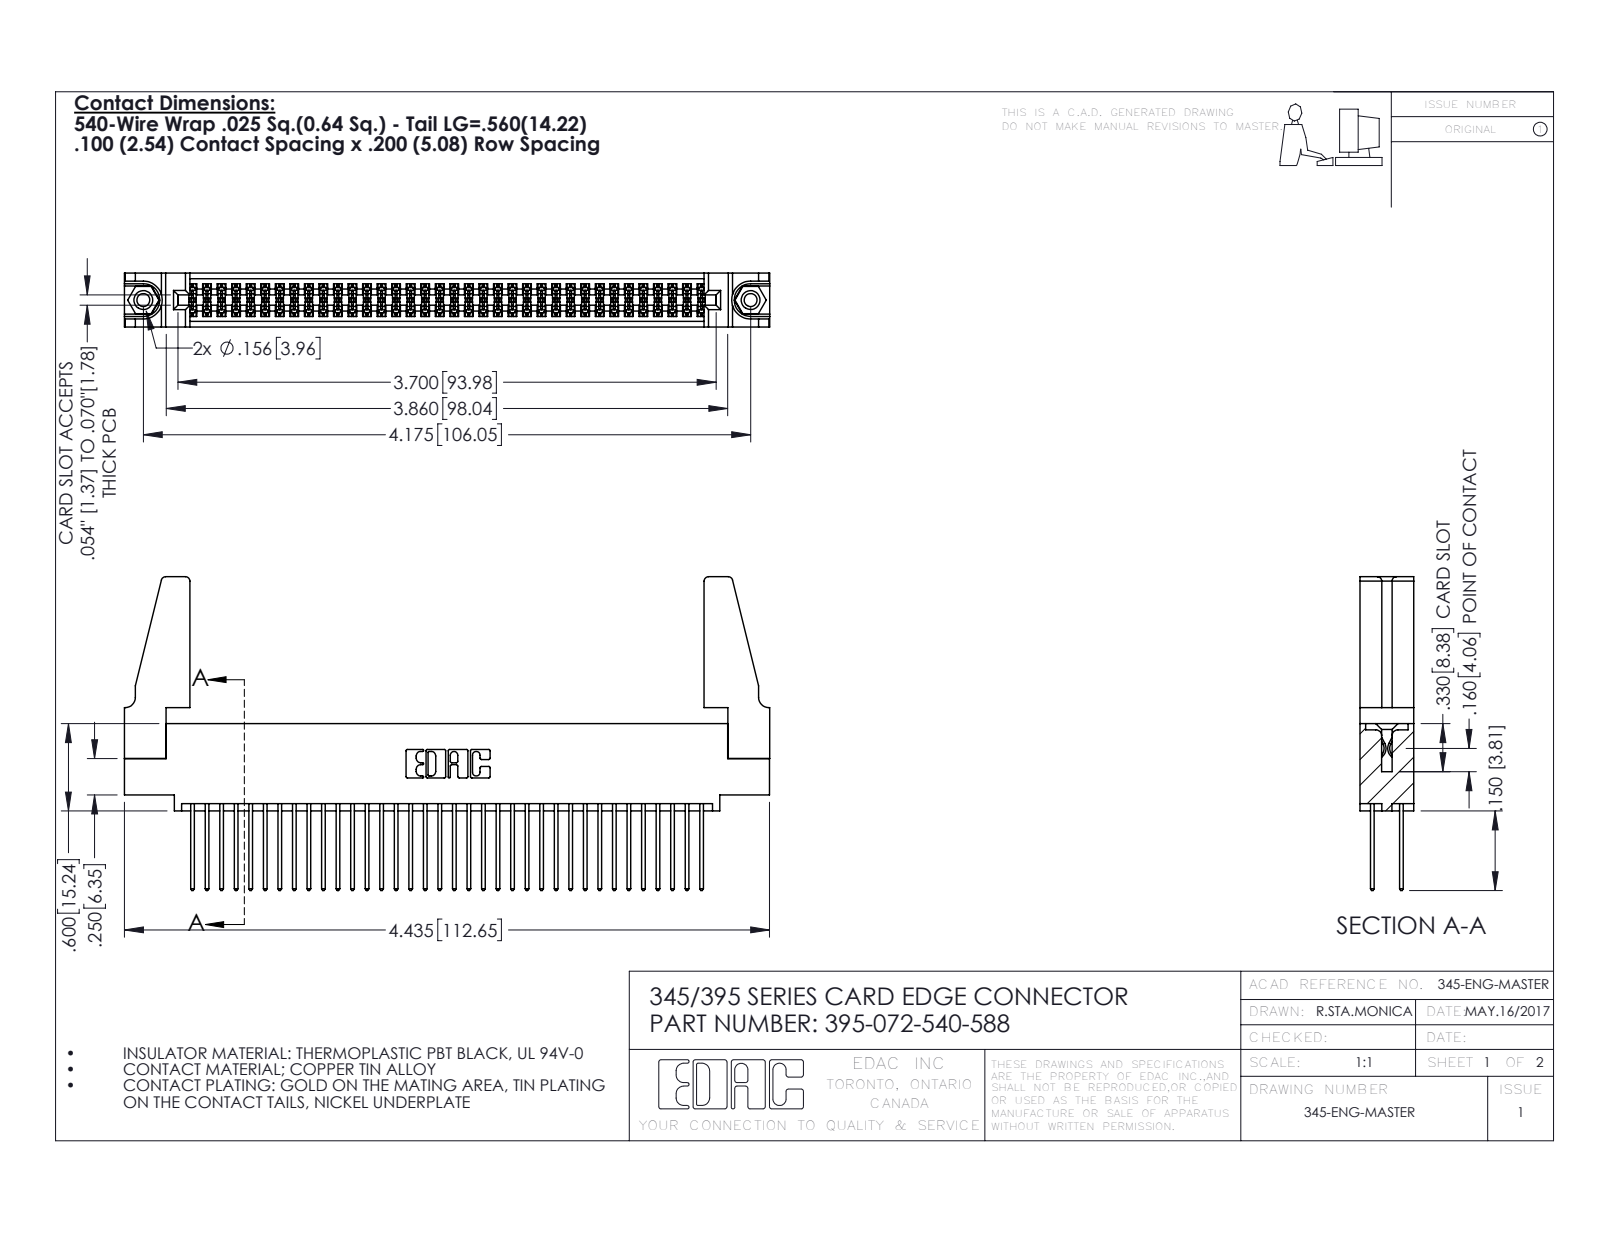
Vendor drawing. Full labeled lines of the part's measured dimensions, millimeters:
Part name (STEP PRODUCT): 345 Part_0.110 Offset - 0.156 Dia-TH; 345-220-078_345-220-088; 345-250-001_345-250-001-102; 345-292-001_345-293-140 (+1 more)
STEP written by: SolidWorks 2016 (CONFIG_CONTROL_DESIGN)
Units: millimetres
Bodies: 77 solids, 3854 faces (2532 planar, 1306 cylindrical, 16 other)
Overall size (bounding box): 112.7 × 54.8 × 9.4
Volume: 14 300 mm³ · Surface area: 20 750 mm²
Round holes (diameter × count): ⌀2.3 ×2, ⌀3.2 ×2, ⌀4 ×2, ⌀1.6 ×1
Round bosses / shafts (diameter × count): ⌀3.9 ×2
Partial cylindrical surfaces — rounded edges, fillets, slot ends (radius × count): R0.2 ×108, R0.3 ×72, R0.3 ×22, R0.8 ×8, R0.2 ×6, R0.8 ×6, R0.7 ×3, R0.4 ×2
Main face-to-face distances: 1.8, 7.6, 5.1, 9.4, 2.5, 6.9, 0.6, 5.7, 4.4, 3.8
Hole centre spacings: 6.9, 100.1, 106
